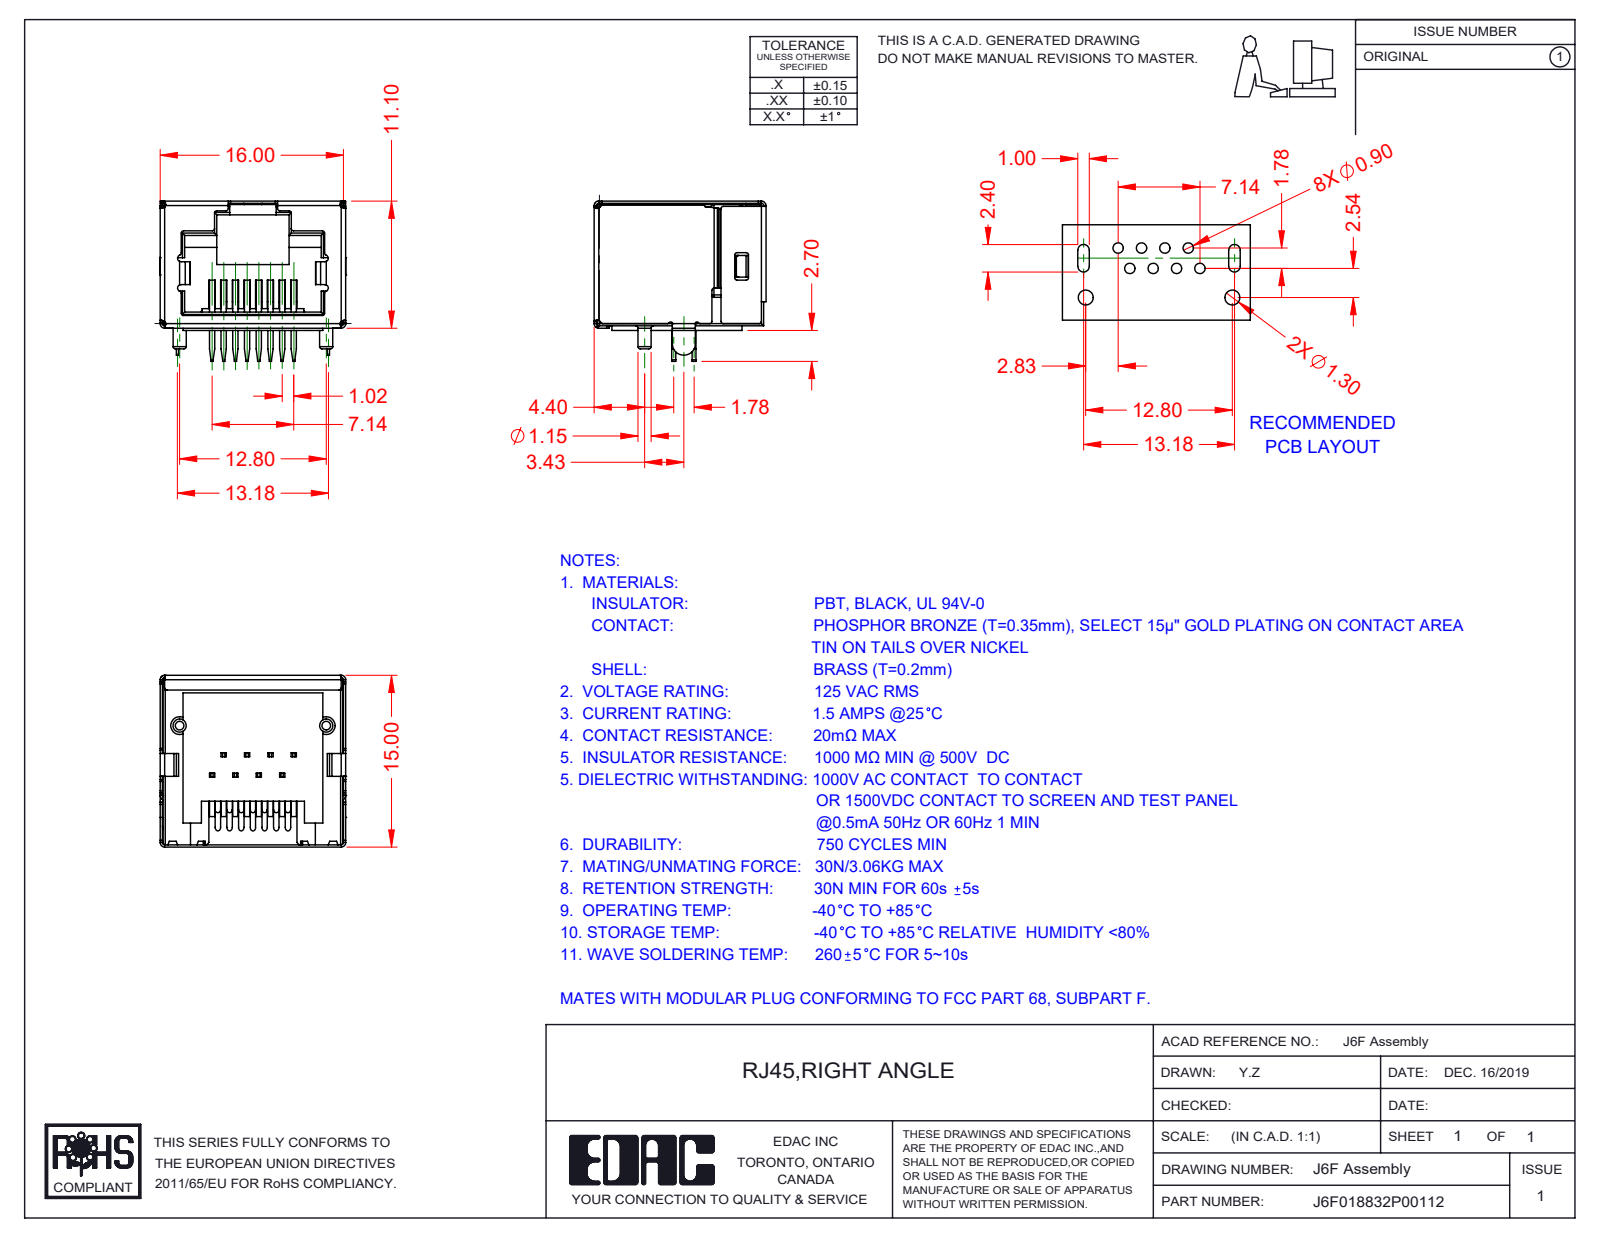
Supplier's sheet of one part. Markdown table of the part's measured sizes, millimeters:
| quantity | value |
| --- | --- |
| part name | J6F018832P00112; 6F Contacts; 6F Shield; 6F Insulator |
| STEP written by | SolidWorks 2016 (CONFIG_CONTROL_DESIGN) |
| units | millimeters |
| bodies | 10 solids, 960 faces (695 planar, 223 cylindrical, 42 other) |
| overall size | 16.2 × 15 × 14 |
| volume | 1 336 mm³ |
| surface area | 3 711 mm² |
| round bosses / shafts (diameter × count) | 1.15 × 2 |
| partial cylindrical surfaces (radius × count) | 0.2 × 77, 0.4 × 24, 0.3 × 20, 0.5 × 9, 0.23 × 7, 0.15 × 5, 0.1 × 4, 1 × 3 |
| main face-to-face distances | 15.75, 16, 15.95, 11, 15.7, 9.7, 11.1, 16.2, 15.8, 1.2 |
